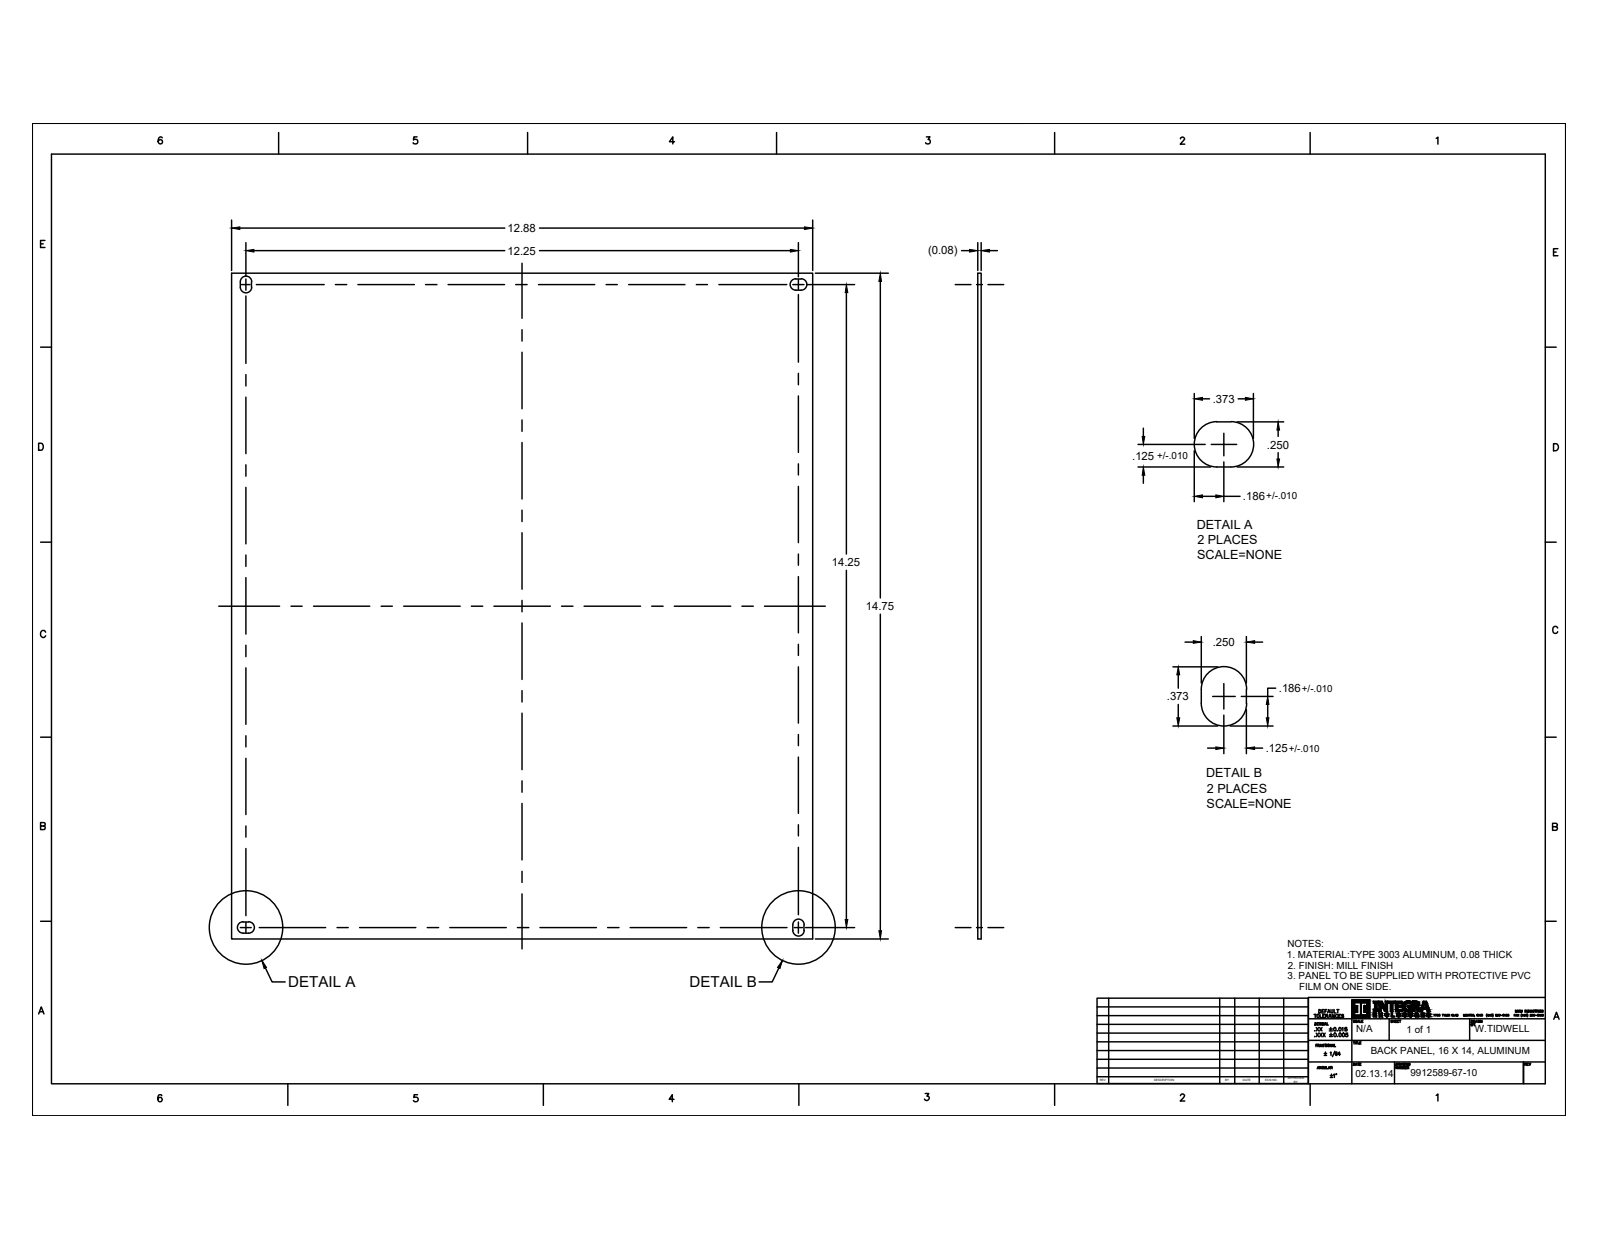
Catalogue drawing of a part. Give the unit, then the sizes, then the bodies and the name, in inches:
Units: inches
Overall size (bounding box): 14.75 × 12.88 × 0.08
Partial cylindrical surfaces — rounded edges, fillets, slot ends (radius × count): R0.125 ×8
Main face-to-face distances: 0.08, 12.88, 14.75, 0.25, 0.19, 0.44, 12.44, 12.69, 12.25, 0.125
Volume: 15.17 in³ · Surface area: 384.1 in²
Bodies: 1 solid, 22 faces (14 planar, 8 cylindrical, 0 other)
Part name (STEP PRODUCT): ABP-1614-P10
STEP written by: SolidWorks 2018 (AUTOMOTIVE_DESIGN)
